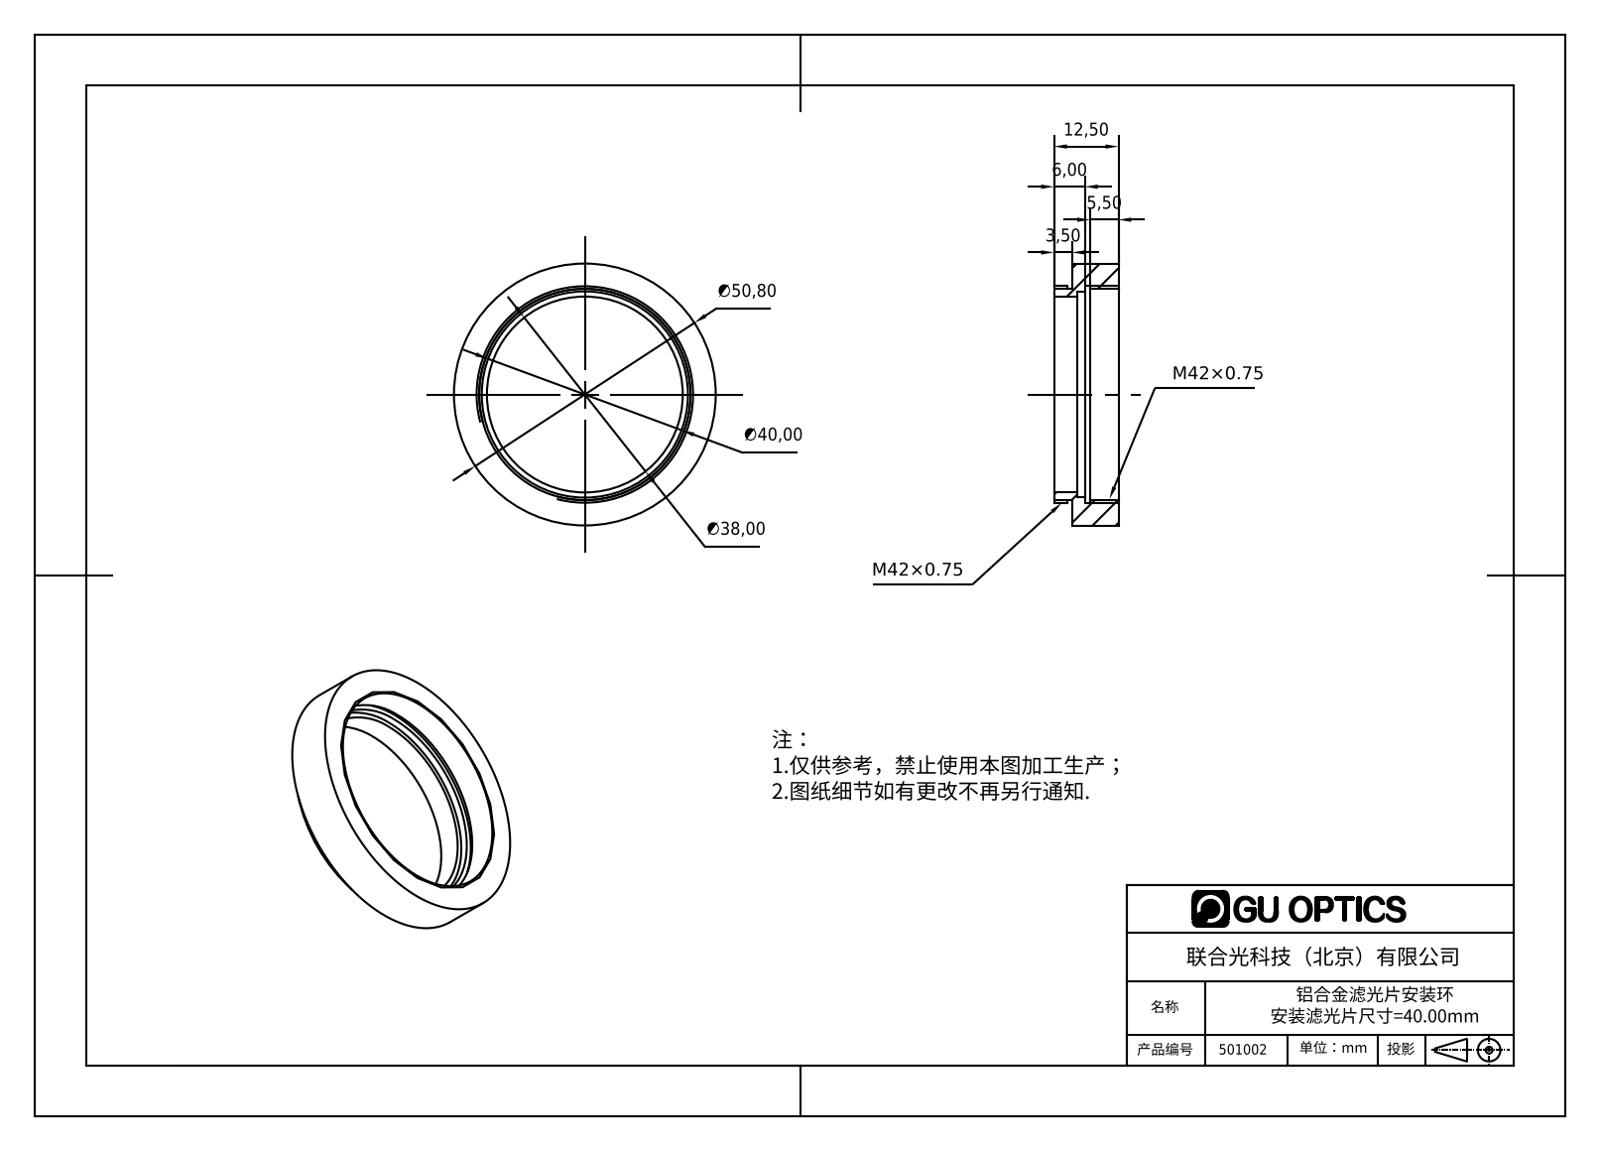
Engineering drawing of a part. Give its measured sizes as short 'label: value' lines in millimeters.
name: 501002
written by: SolidWorks 2016 (CONFIG_CONTROL_DESIGN)
unit: mm
bodies: 1 solid, 21 faces (7 planar, 14 cylindrical, 0 other)
size: 50.8 × 50.8 × 12.5
volume: 7 377 mm³; area: 5 534 mm²
holes: 1× ⌀38, 1× ⌀40, 1× ⌀41, 1× ⌀42.2
bosses: 1× ⌀50.8, 1× ⌀42
face distances: 9, 3.5, 2.5, 1, 12.5, 4.5, 6, 6.5, 1.5, 8
